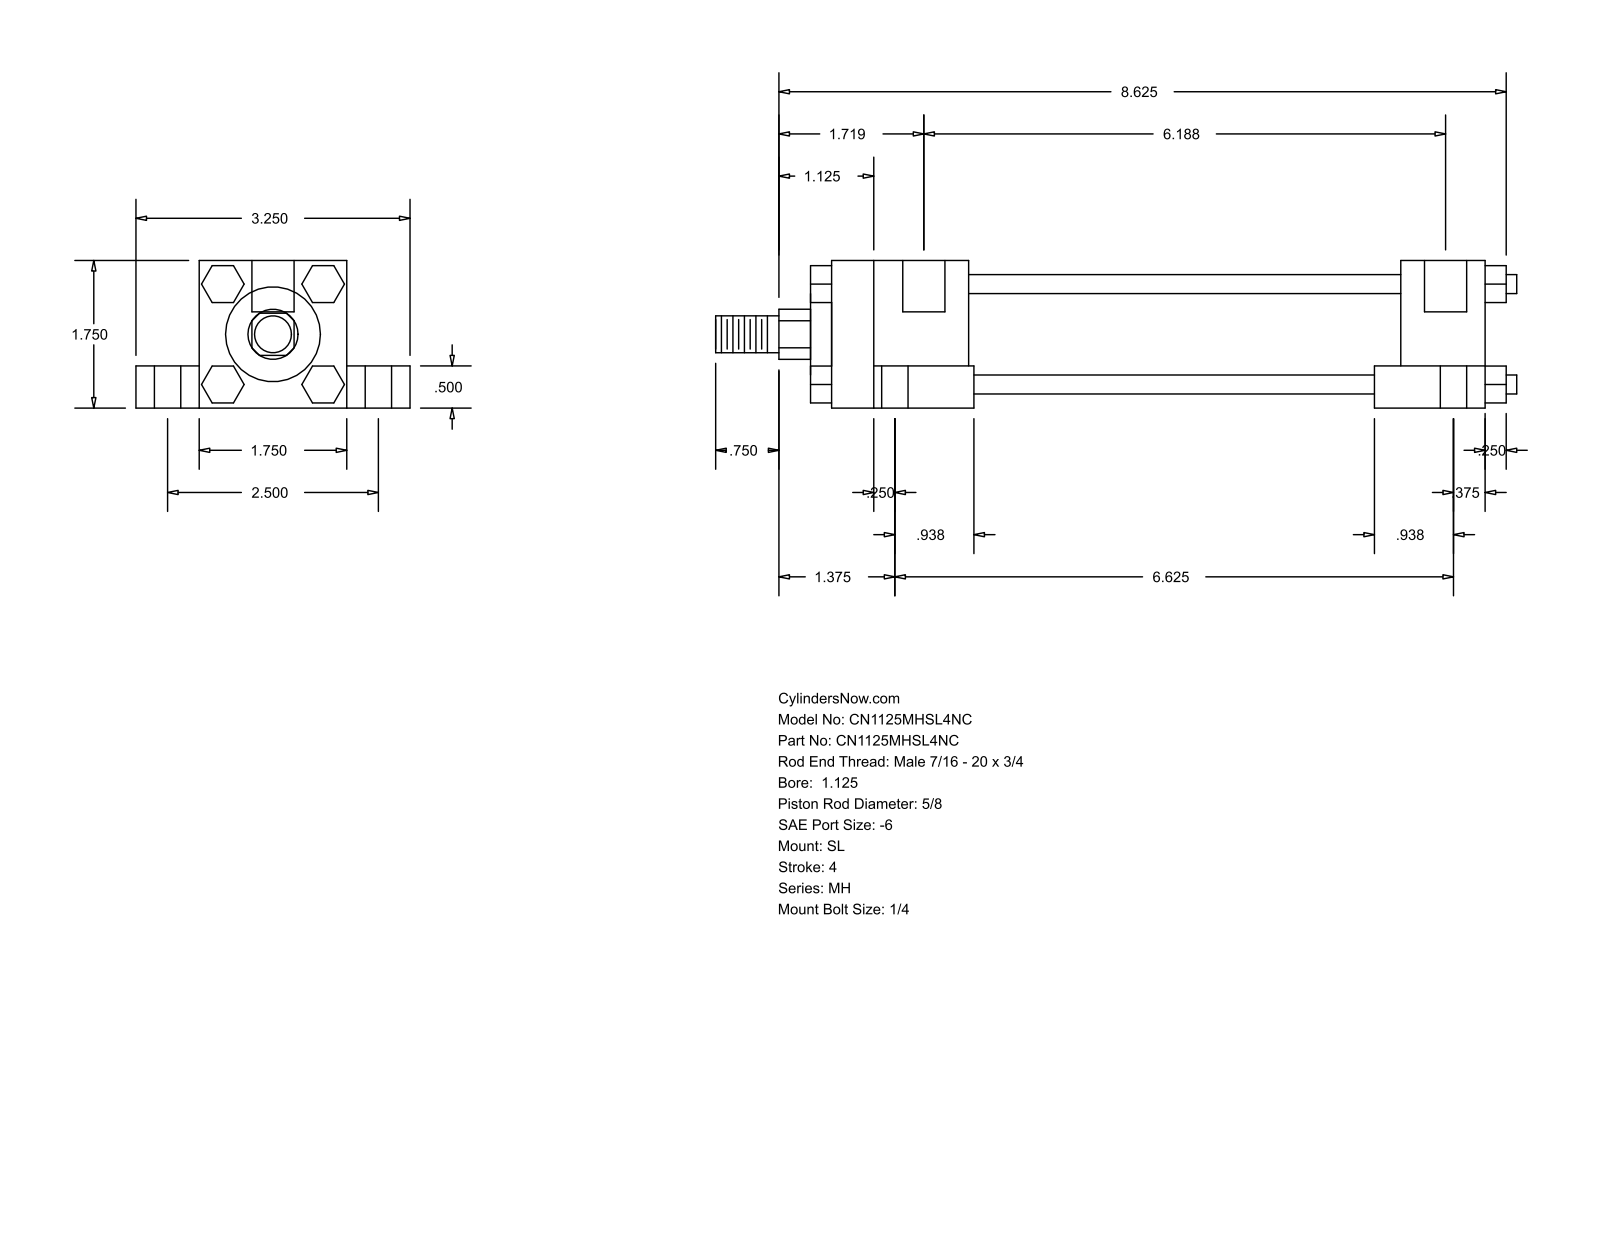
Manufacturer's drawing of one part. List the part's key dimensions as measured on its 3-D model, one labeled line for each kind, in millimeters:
Part name (STEP PRODUCT): MH_SL__0112_0.625
STEP written by: GSSL Pune (CONFIG_CONTROL_DESIGN)
Units: millimetres
Bodies: 0 solids, 150 faces (114 planar, 36 cylindrical, 0 other)
Overall size (bounding box): 241.3 × 82.55 × 44.45
Round holes (diameter × count): ⌀5.56 ×4, ⌀7.94 ×4, ⌀14.29 ×4, ⌀12.7 ×2
Round bosses / shafts (diameter × count): ⌀5.71 ×4, ⌀34.92 ×1, ⌀28.57 ×1, ⌀15.88 ×1, ⌀11.11 ×1
Partial cylindrical surfaces — rounded edges, fillets, slot ends (radius × count): R7.54 ×1
Main face-to-face distances: 44.46, 19.04, 12.7, 31.76, 63.5, 6.35, 203.19, 11.11, 47.62, 25.4
Hole centre spacings: 31.84, 32.23, 32.93, 63.5, 153.99, 159.56, 162.67, 165.1
